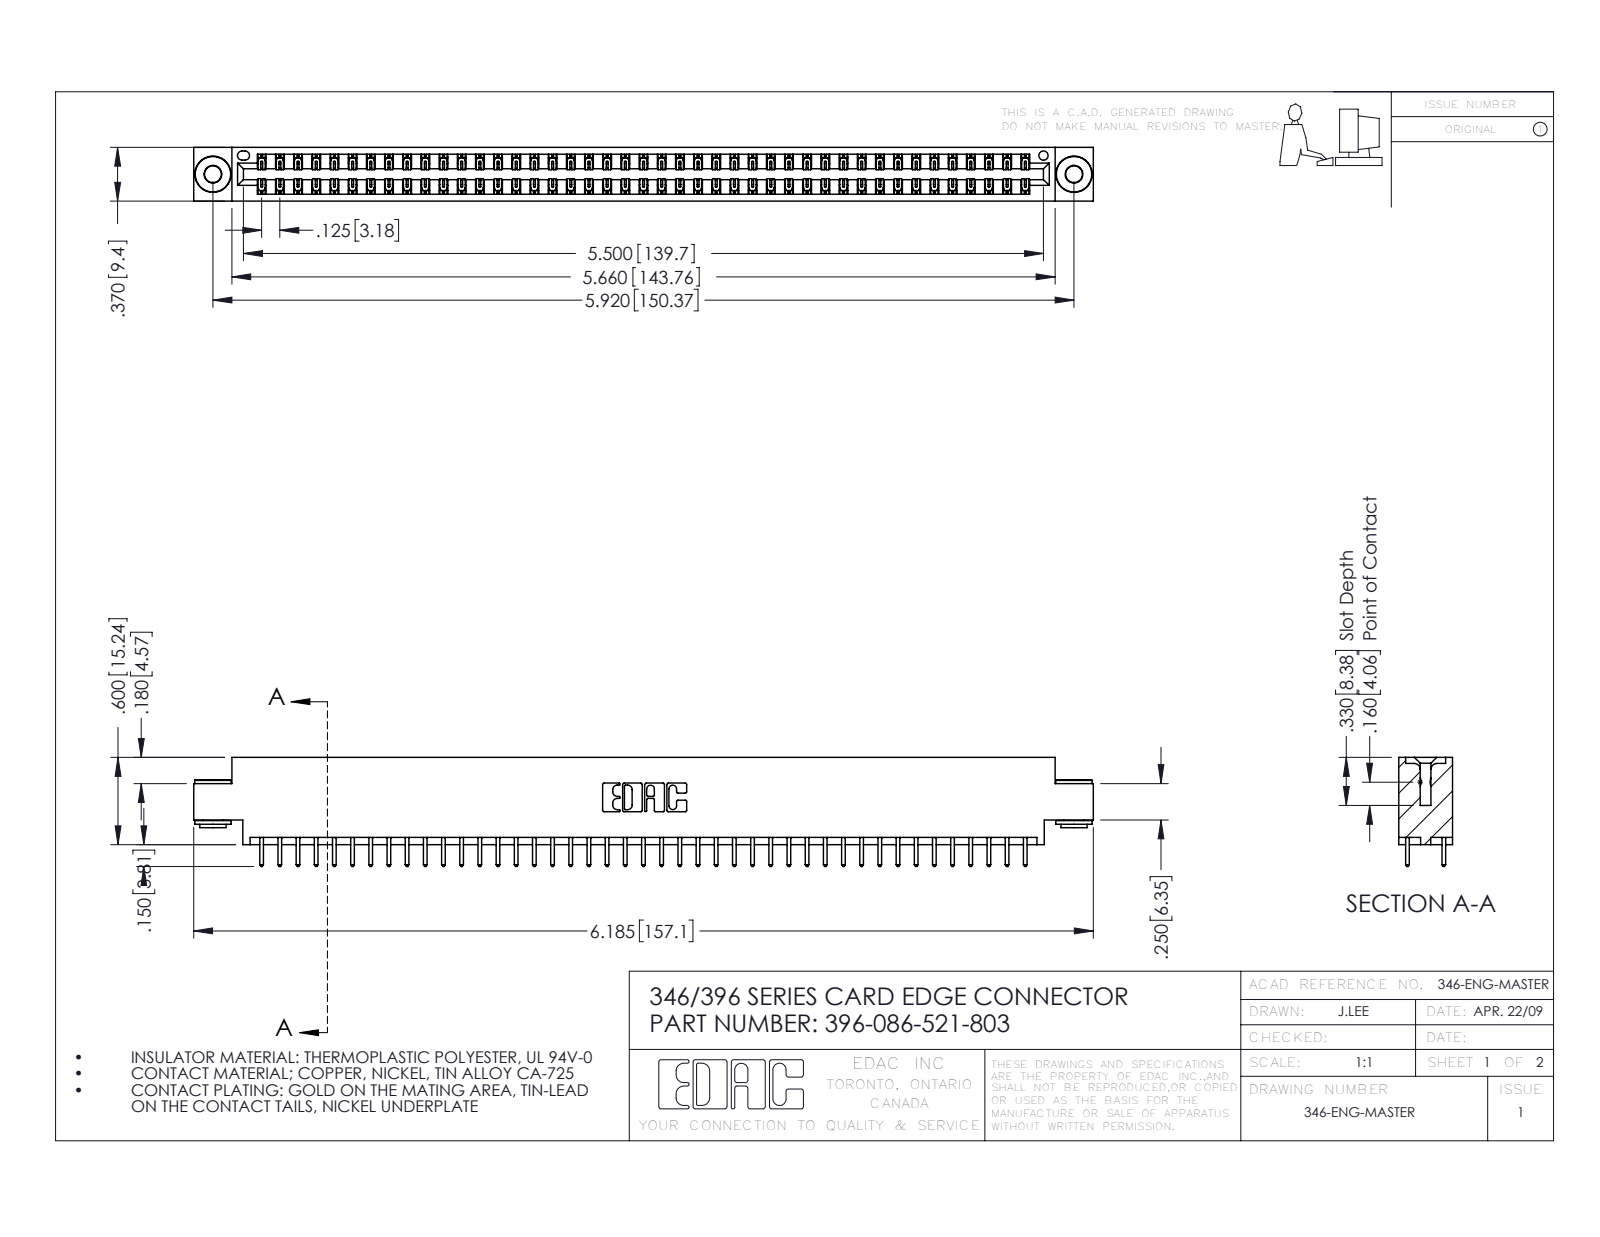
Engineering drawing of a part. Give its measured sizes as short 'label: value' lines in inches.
name: 345-250-002_345-250-002-102; 396-086-521-803; 346 Part_0.170 Offset - 0.156 Dia-TH; 345-292-001_345-293-121
written by: SolidWorks 2016 (CONFIG_CONTROL_DESIGN)
unit: in
bodies: 89 solids, 4636 faces (3100 planar, 1528 cylindrical, 8 other)
size: 6.185 × 0.75 × 0.37
volume: 0.925 in³; area: 32.56 in²
holes: 2× ⌀0.116, 2× ⌀0.156, 1× ⌀0.064
bosses: 2× ⌀0.25, 2× ⌀0.18, 2× ⌀0.136
rounds: 129× R0.006, 86× R0.01, 22× R0.01, 6× R0.007, 6× R0.031, 3× R0.026, 2× R0.014, 2× R0.022
face distances: 0.048, 0.322, 0.37, 0.25, 0.025, 0.072, 0.298, 0.275, 0.148, 0.222
hole spacings: 0.246, 5.711, 5.92
